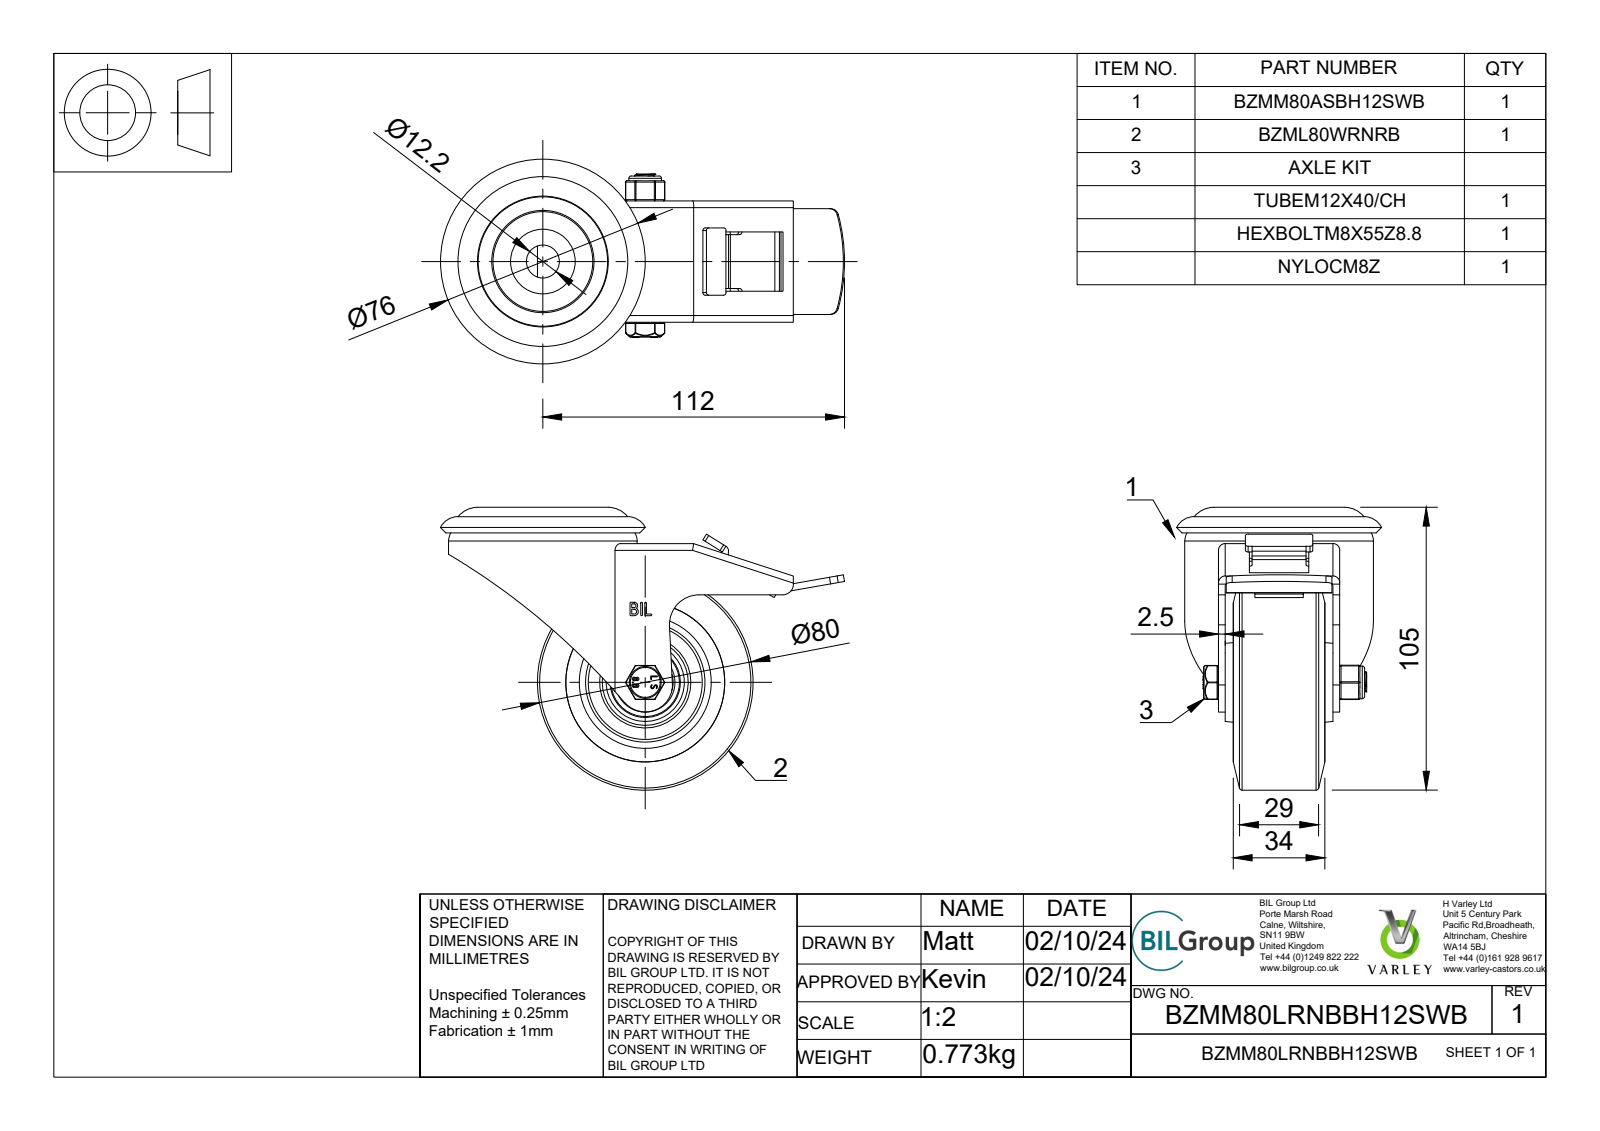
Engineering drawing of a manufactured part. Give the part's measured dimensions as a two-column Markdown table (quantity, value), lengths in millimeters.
| quantity | value |
| --- | --- |
| part name | BZMM80LRNBBH12SWB v3; BZMM80ASBH12SWB v1; ZINC PLATED, PRESSED STEEL HEAD; ZINC PLATED, PRESSED STEEL FORKS (+8 more) |
| STEP written by | Autodesk Translation Framework v13.20.0.188 (AUTOMOTIVE_DESIGN) |
| units | millimeters |
| bodies | 19 solids, 686 faces (342 planar, 238 cylindrical, 106 other) |
| overall size | 150 × 105 × 76 |
| volume | 207 568 mm³ |
| surface area | 108 032 mm² |
| round holes (diameter × count) | 0.66 × 2, 8 × 1, 8.2 × 1, 8.4 × 1, 8.6 × 1, 12.2 × 1, 12.5 × 1, 20 × 1, 26 × 1, 59 × 1, 65 × 1, 72 × 1 |
| round bosses / shafts (diameter × count) | 3.75 × 8, 80 × 1, 70 × 1, 49.5 × 1, 38 × 1, 24 × 1, 21.31 × 1, 19.5 × 1 |
| partial cylindrical surfaces (radius × count) | 0.75 × 48, 0.5 × 26, 0.25 × 12, 1 × 6, 1.25 × 6, 2 × 5, 2.5 × 5, 0.33 × 4 |
| main face-to-face distances | 2.5, 42.5, 5.5, 3, 40, 4.5, 45, 8, 39.5, 37 |
| hole center spacings | 3.22, 2.49 |
